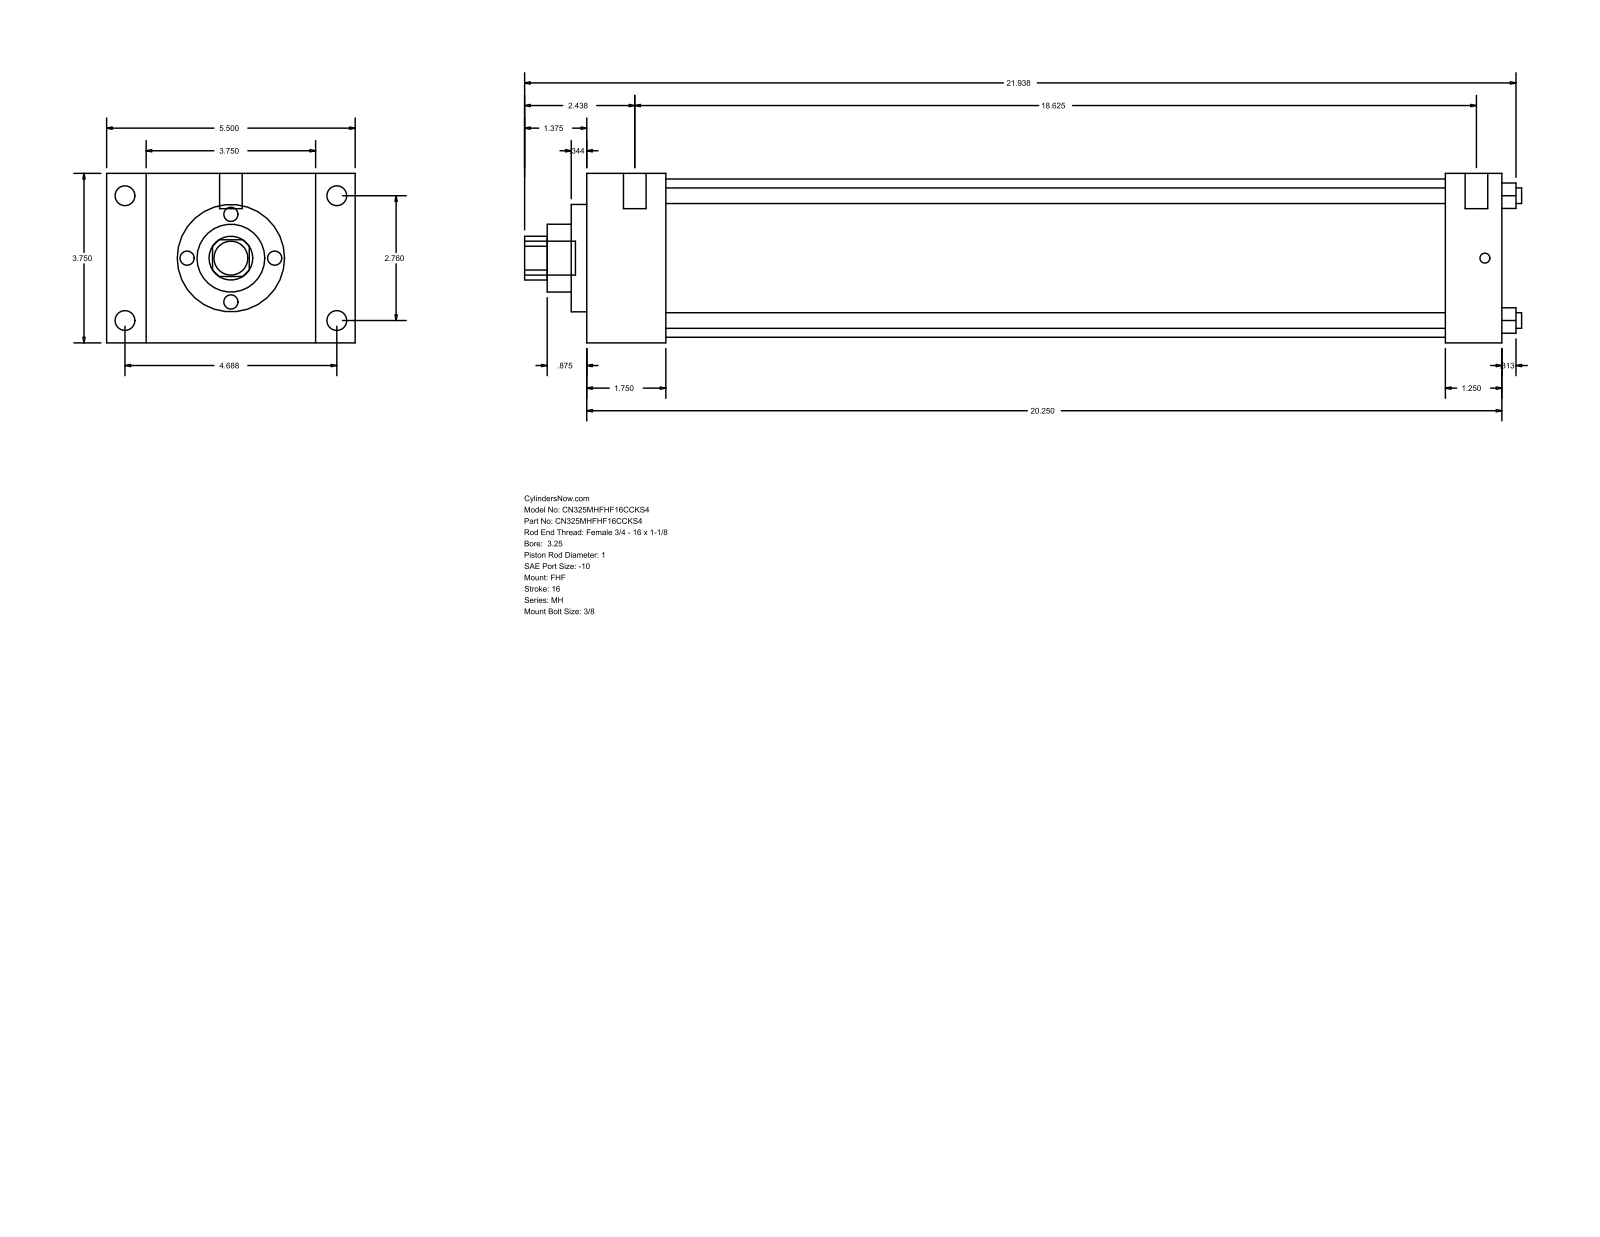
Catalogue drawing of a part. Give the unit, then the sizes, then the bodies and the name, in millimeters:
Units: millimetres
Overall size (bounding box): 560.39 × 139.7 × 95.25
Round holes (diameter × count): ⌀8.76 ×4, ⌀25.4 ×1, ⌀38.1 ×1, ⌀60.33 ×1, ⌀88.9 ×1
Round bosses / shafts (diameter × count): ⌀11.13 ×4, ⌀5.56 ×4, ⌀12.7 ×2, ⌀19.05 ×1
Partial cylindrical surfaces — rounded edges, fillets, slot ends (radius × count): R12.29 ×1
Main face-to-face distances: 95.24, 514.35, 44.46, 469.89, 22.23, 117.47, 139.7, 482.6, 438.14, 31.75
Hole centre spacings: 49.57, 70.1, 99.14
Bodies: 0 solids, 90 faces (61 planar, 29 cylindrical, 0 other)
Part name (STEP PRODUCT): MH_FHF__0325_1
STEP written by: GSSL Pune (CONFIG_CONTROL_DESIGN)
